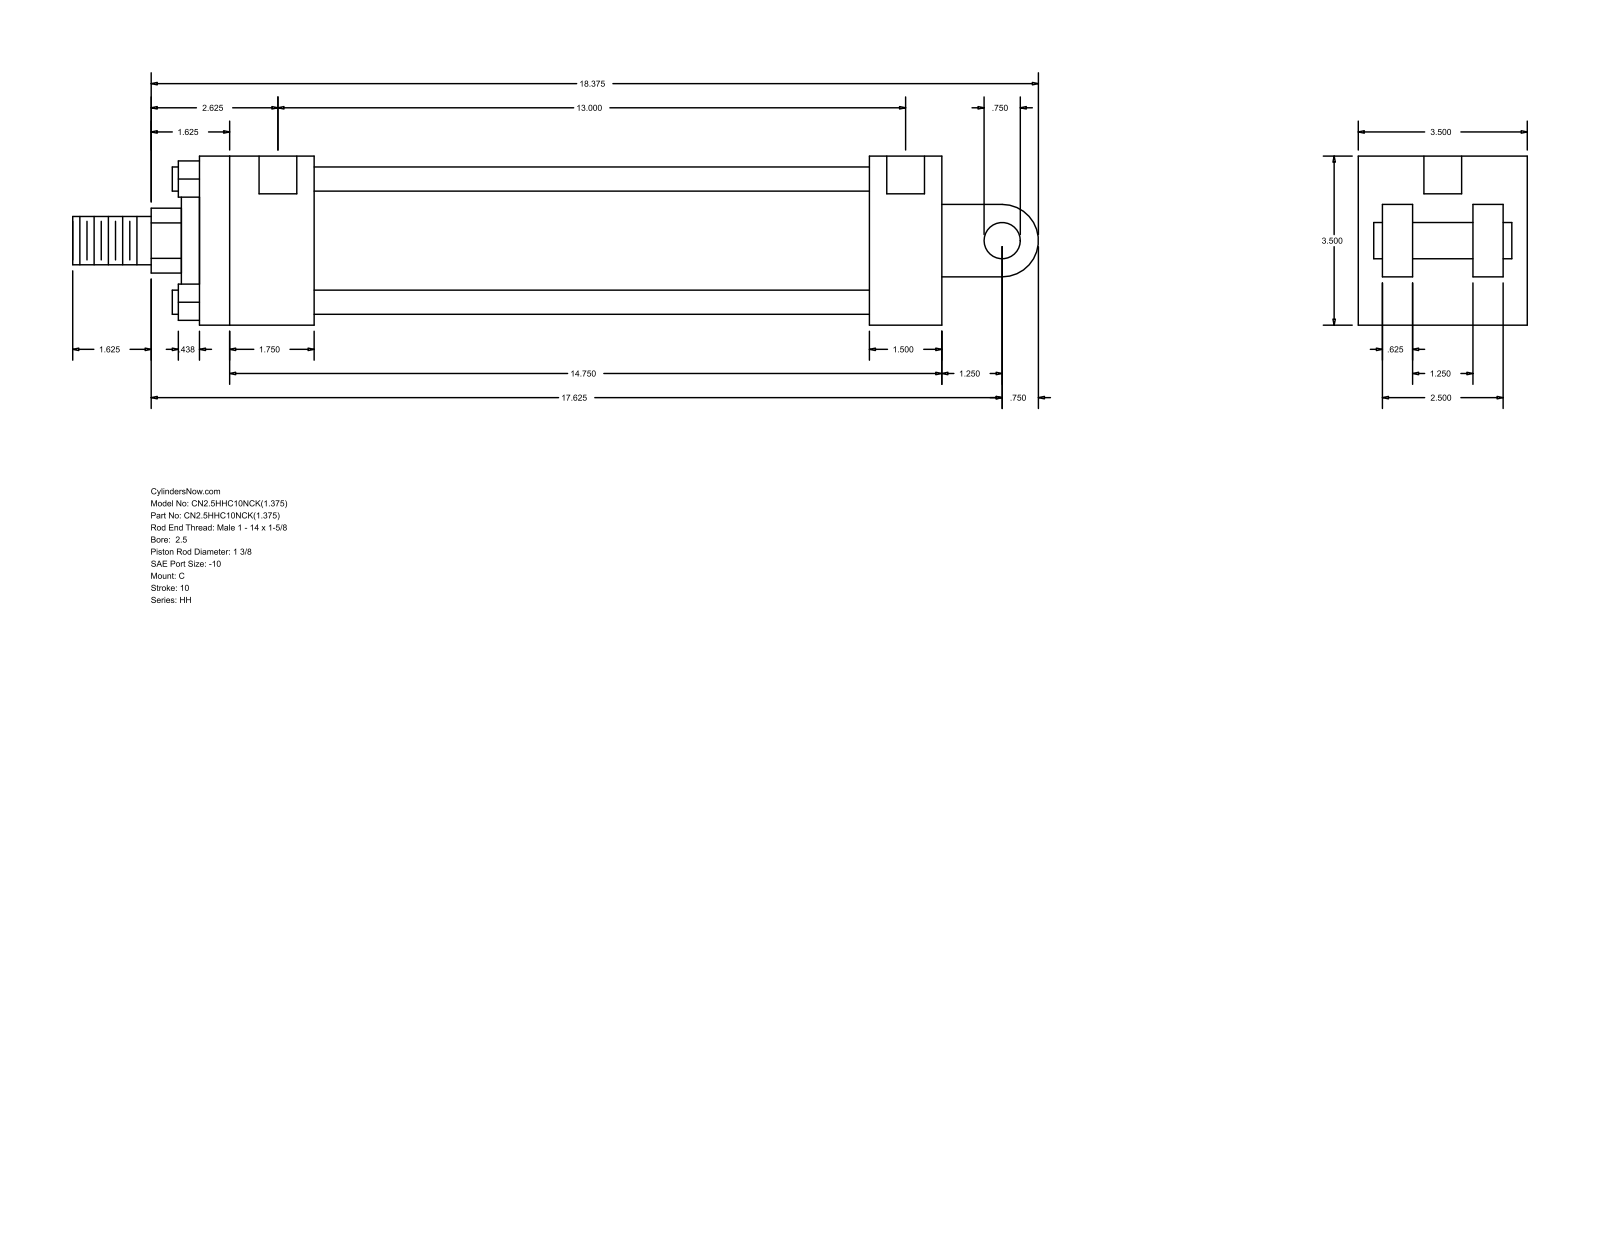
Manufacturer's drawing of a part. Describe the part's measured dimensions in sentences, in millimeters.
The part is named "HH_C__0250_1.375". Its 3-D file was written by "GSSL Pune (CONFIG_CONTROL_DESIGN)". It is 0 solids with 99 faces: 70 planar, 29 cylindrical and 0 other. Overall it measures 508 by 88.9 by 88.9 millimeters. Round holes: 4 of diameter 5.56, 2 of diameter 19.84. Round bosses or shafts: 4 of diameter 12.7, 1 of diameter 73.03, 1 of diameter 50.8, 1 of diameter 34.92, 1 of diameter 25.4, 1 of diameter 19.05. Partial cylindrical surfaces (rounded edges, fillets, slot ends): 1 of radius 17.06, 1 of radius 19.05. The main face-to-face distances are 88.9, 390.53, 63.5, 12.7, 352.42, 38.11, 60.32, 292.1, 330.21, 76.2. The hole center spacings are 1.58, 331.79, 333.37, 330.21.
